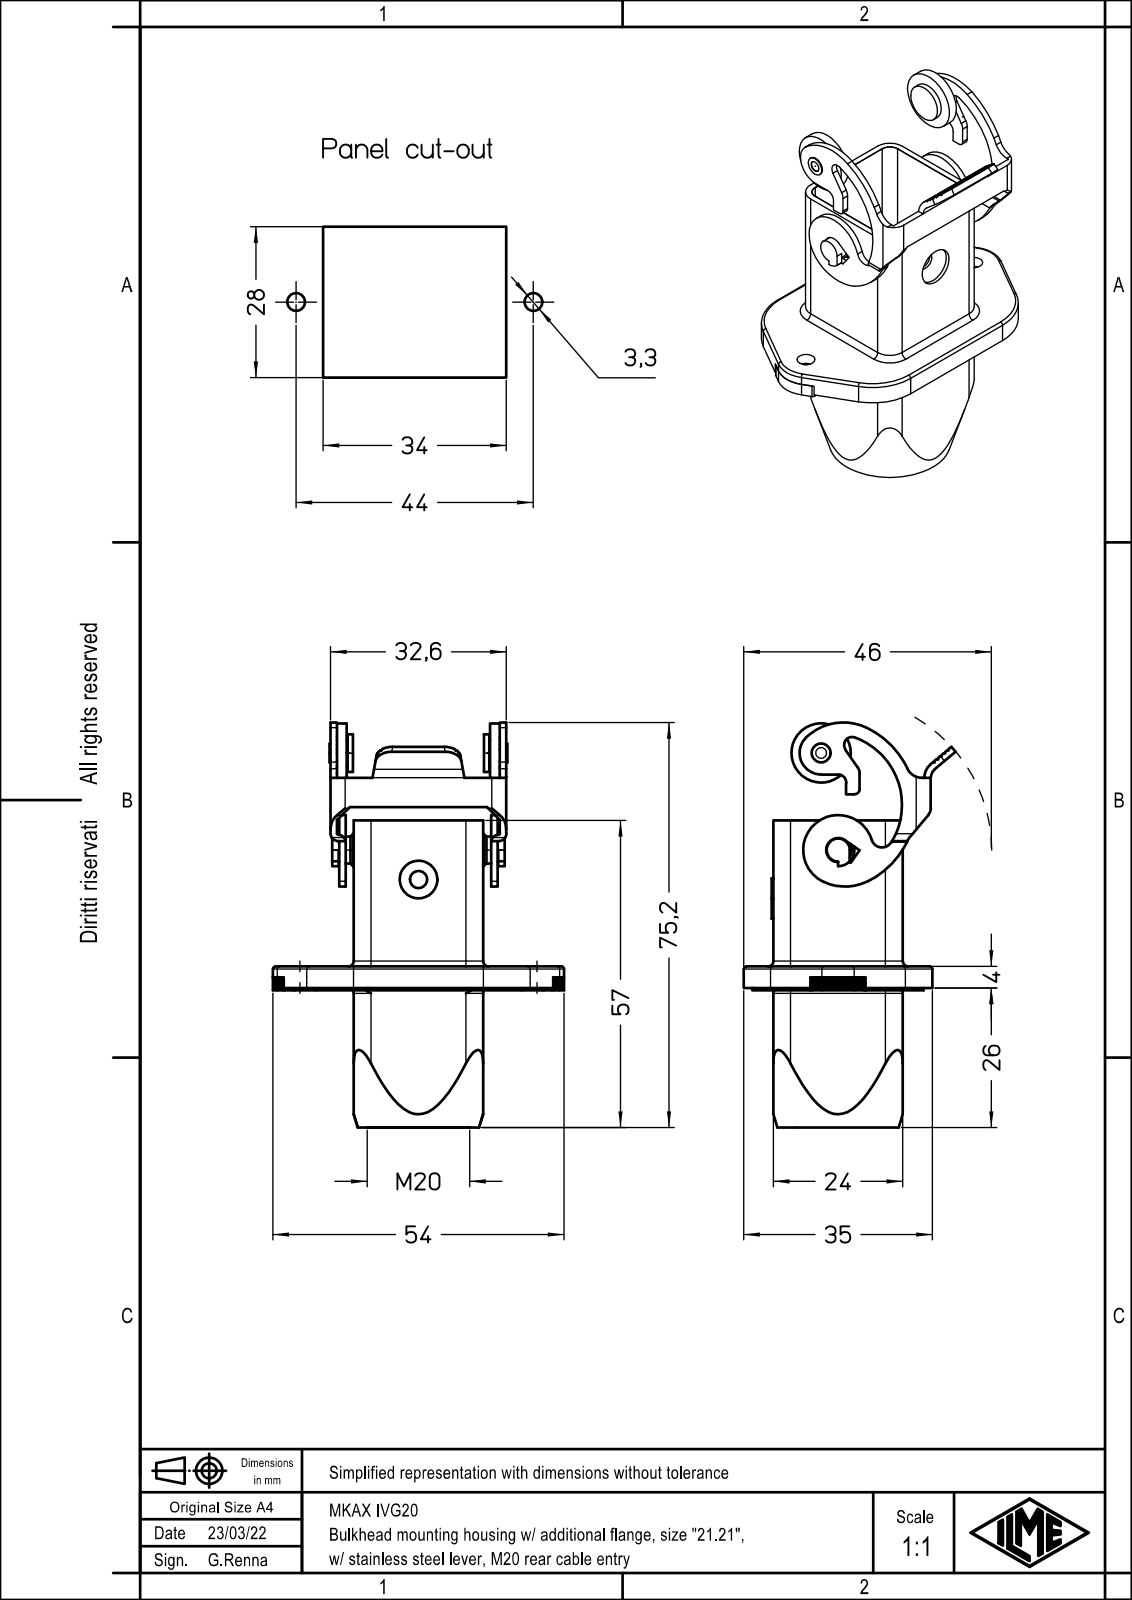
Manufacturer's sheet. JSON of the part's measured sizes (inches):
{"part_name": "MKA_IVG20; MKAX_IVG20", "step_written_by": "Creo Elements/Direct Modeling 20.1B 02-Apr-2019 (C) Parametric Technology GmbH (AUTOMOTIVE_DESIGN)", "units": "inches", "bodies": {"solids": 1, "faces": 454, "planar": 229, "cylindrical": 185, "other": 40}, "overall_size": [2.959, 2.126, 1.547], "volume_in3": 0.905, "surface_area_in2": 24.88, "round_holes": [[0.102, 2], [0.13, 2], [0.079, 1], [0.126, 1], [0.197, 1], [0.276, 1], [0.63, 1], [0.717, 1]], "round_bosses_or_shafts": [[0.433, 1], [0.276, 1], [0.236, 1], [0.197, 1], [0.189, 1], [0.169, 1], [0.138, 1]], "partial_cylinders_radius": [[0.01, 15], [0.02, 15], [0.039, 11], [0.079, 8], [0.197, 8], [0.126, 5], [0.394, 5], [0.008, 4]], "face_to_face_distances": [0.945, 0.047, 0.063, 0.157, 1.173, 0.175, 0.059, 1.102, 1.067, 0.018], "hole_center_spacings": [0.866, 1.732]}
